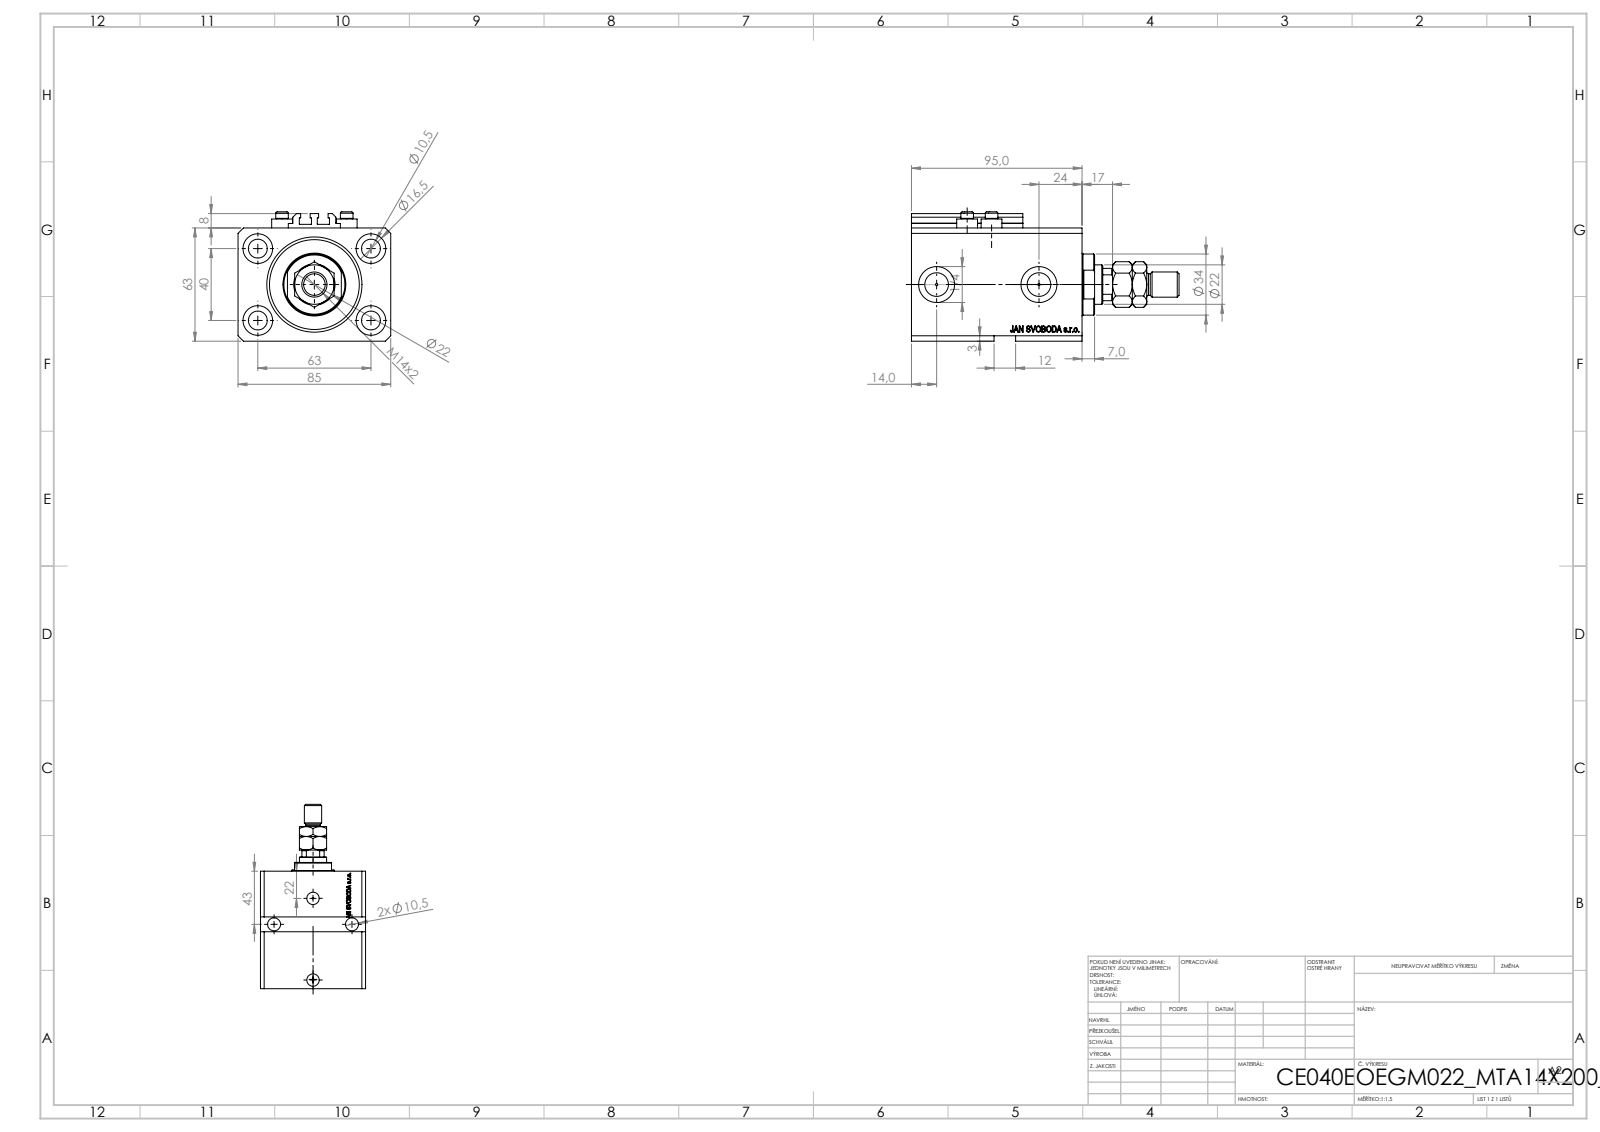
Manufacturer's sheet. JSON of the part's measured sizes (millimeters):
{"part_name": "MTA; V250CE_E_Body; V250CE_VC_E; ALLEN BOLT V250CE (+1 more)", "step_written_by": "SolidWorks 2019 (CONFIG_CONTROL_DESIGN)", "units": "millimeters", "bodies": {"solids": 9, "faces": 1136, "planar": 550, "cylindrical": 130, "other": 456}, "overall_size": [149, 85, 72], "volume_mm3": 456273, "surface_area_mm2": 100261, "round_holes": [[10.5, 6], [1.25, 4], [4, 4], [16.5, 4], [10, 2], [13.16, 2], [20, 2], [12.5, 1], [22, 1], [40, 1], [53, 1]], "round_bosses_or_shafts": [[11.6, 4], [7, 4], [34, 1], [14, 1], [12, 1]], "partial_cylinders_radius": [[0.2, 10], [10.5, 1]], "face_to_face_distances": [63, 85, 17, 95, 78, 11.4, 66.6, 83.6, 3, 22], "hole_center_spacings": [37.31, 63, 13.6, 15.4, 24.96, 29.58, 30, 33.62]}
